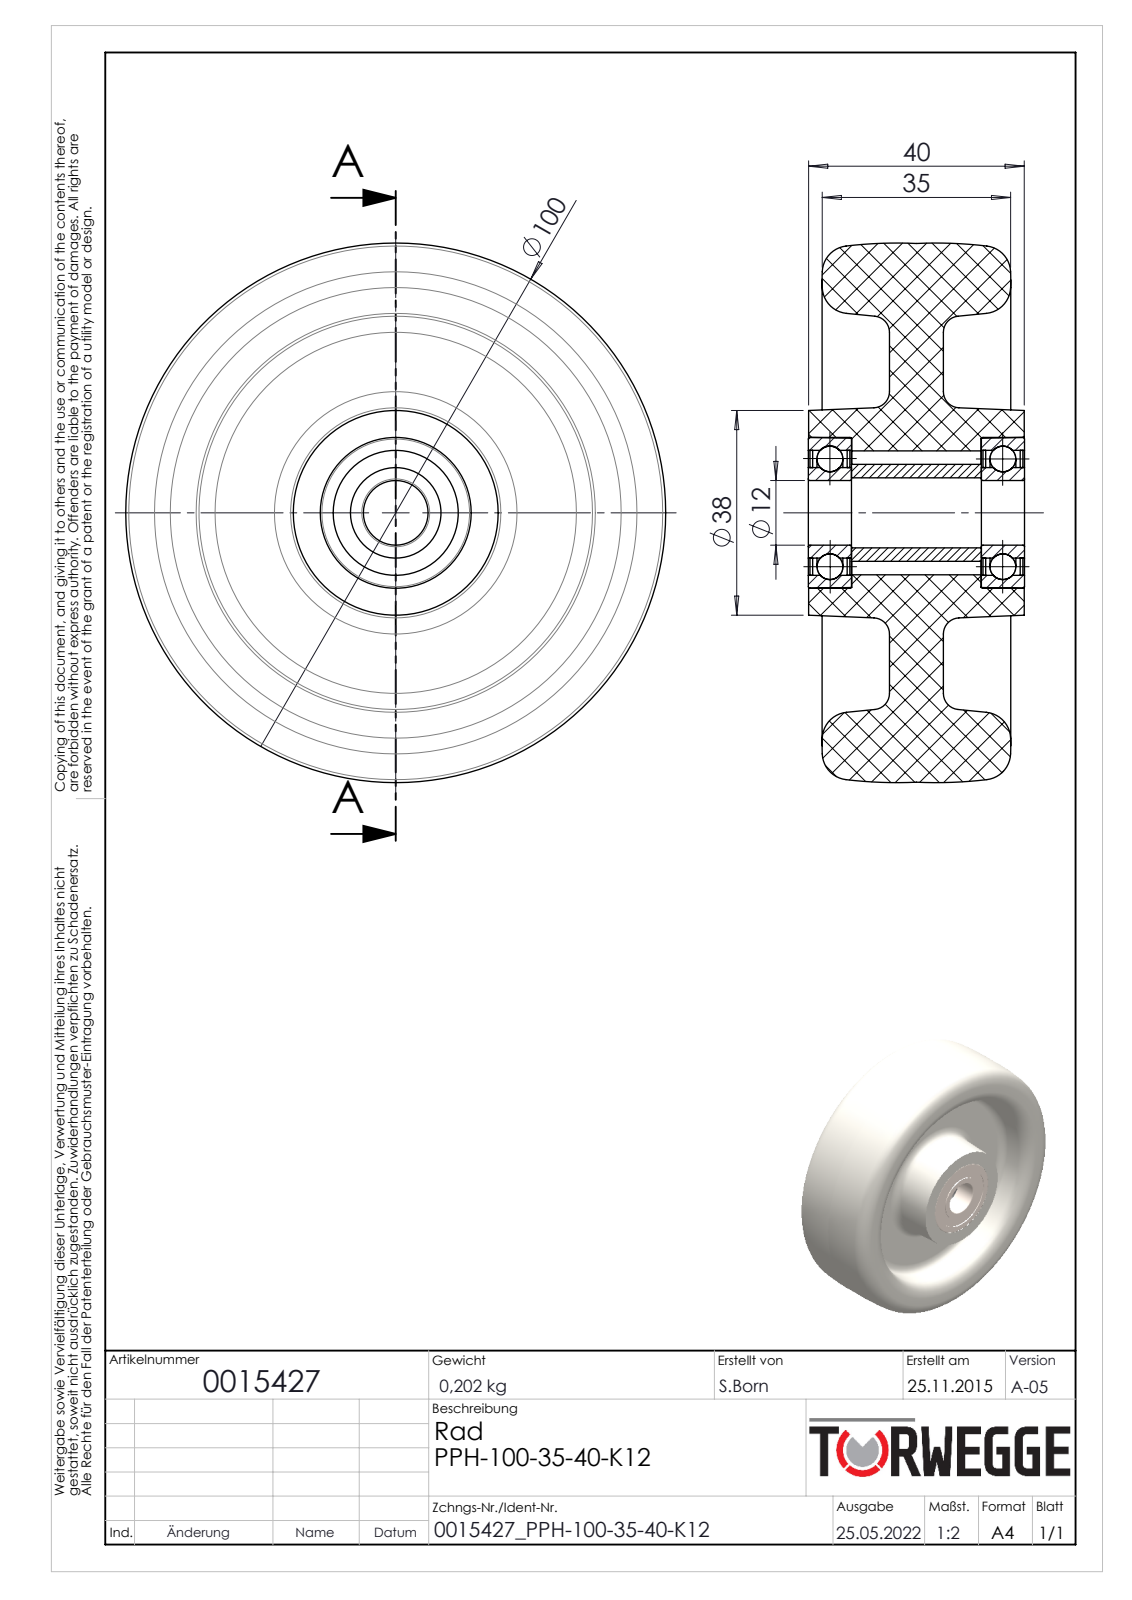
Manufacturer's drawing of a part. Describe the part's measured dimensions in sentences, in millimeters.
The part is named "0015427". Its 3-D file was written by "SolidWorks 2020 (AUTOMOTIVE_DESIGN)". It is 12 solids with 142 faces: 24 planar, 46 cylindrical and 72 other. Overall it measures 100.17 by 100.17 by 40.1 millimeters. Its volume is 187 567 cubic millimeters and its surface area 46 126 square millimeters. Round holes: 1 of diameter 12, 1 of diameter 13, 1 of diameter 16.8, 1 of diameter 23, 1 of diameter 23.2. Round bosses or shafts: 1 of diameter 28, 1 of diameter 18. The main face-to-face distances are 10, 32.1, 32.05, 15, 25, 8, 0.8, 7.2, 7.7, 0.5.
